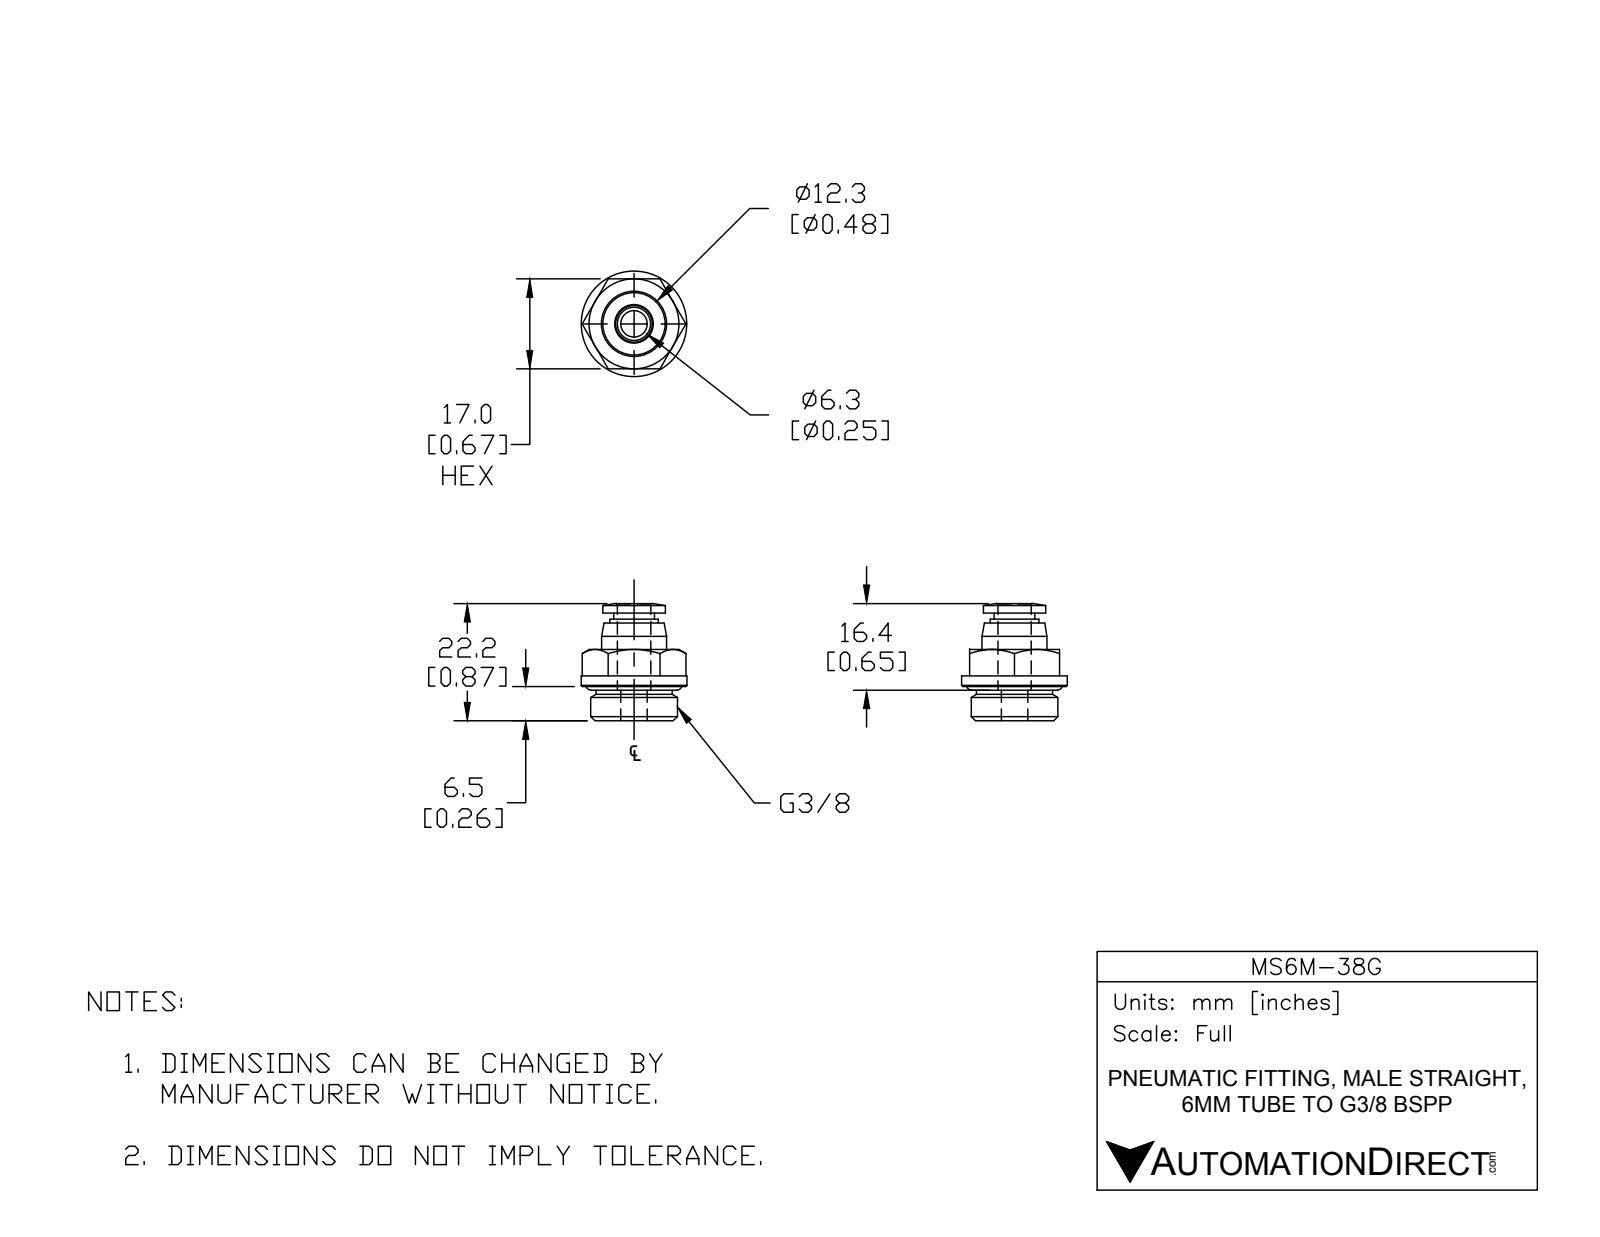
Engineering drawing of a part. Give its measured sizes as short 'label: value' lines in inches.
name: MS6M-38G
written by: SolidWorks 2018 (AUTOMOTIVE_DESIGN)
unit: in
bodies: 2 solids, 59 faces (16 planar, 18 cylindrical, 25 other)
size: 0.874 × 0.787 × 0.787
volume: 0.209 in³; area: 3.962 in²
holes: 1× ⌀0.197, 1× ⌀0.248
bosses: 1× ⌀0.787, 1× ⌀0.646, 1× ⌀0.567, 1× ⌀0.484, 1× ⌀0.465, 1× ⌀0.362, 1× ⌀0.303
face distances: 0.669, 0.531, 0.197, 0.335, 0.803, 0.469, 0.272, 0.075, 0.228, 0.303
